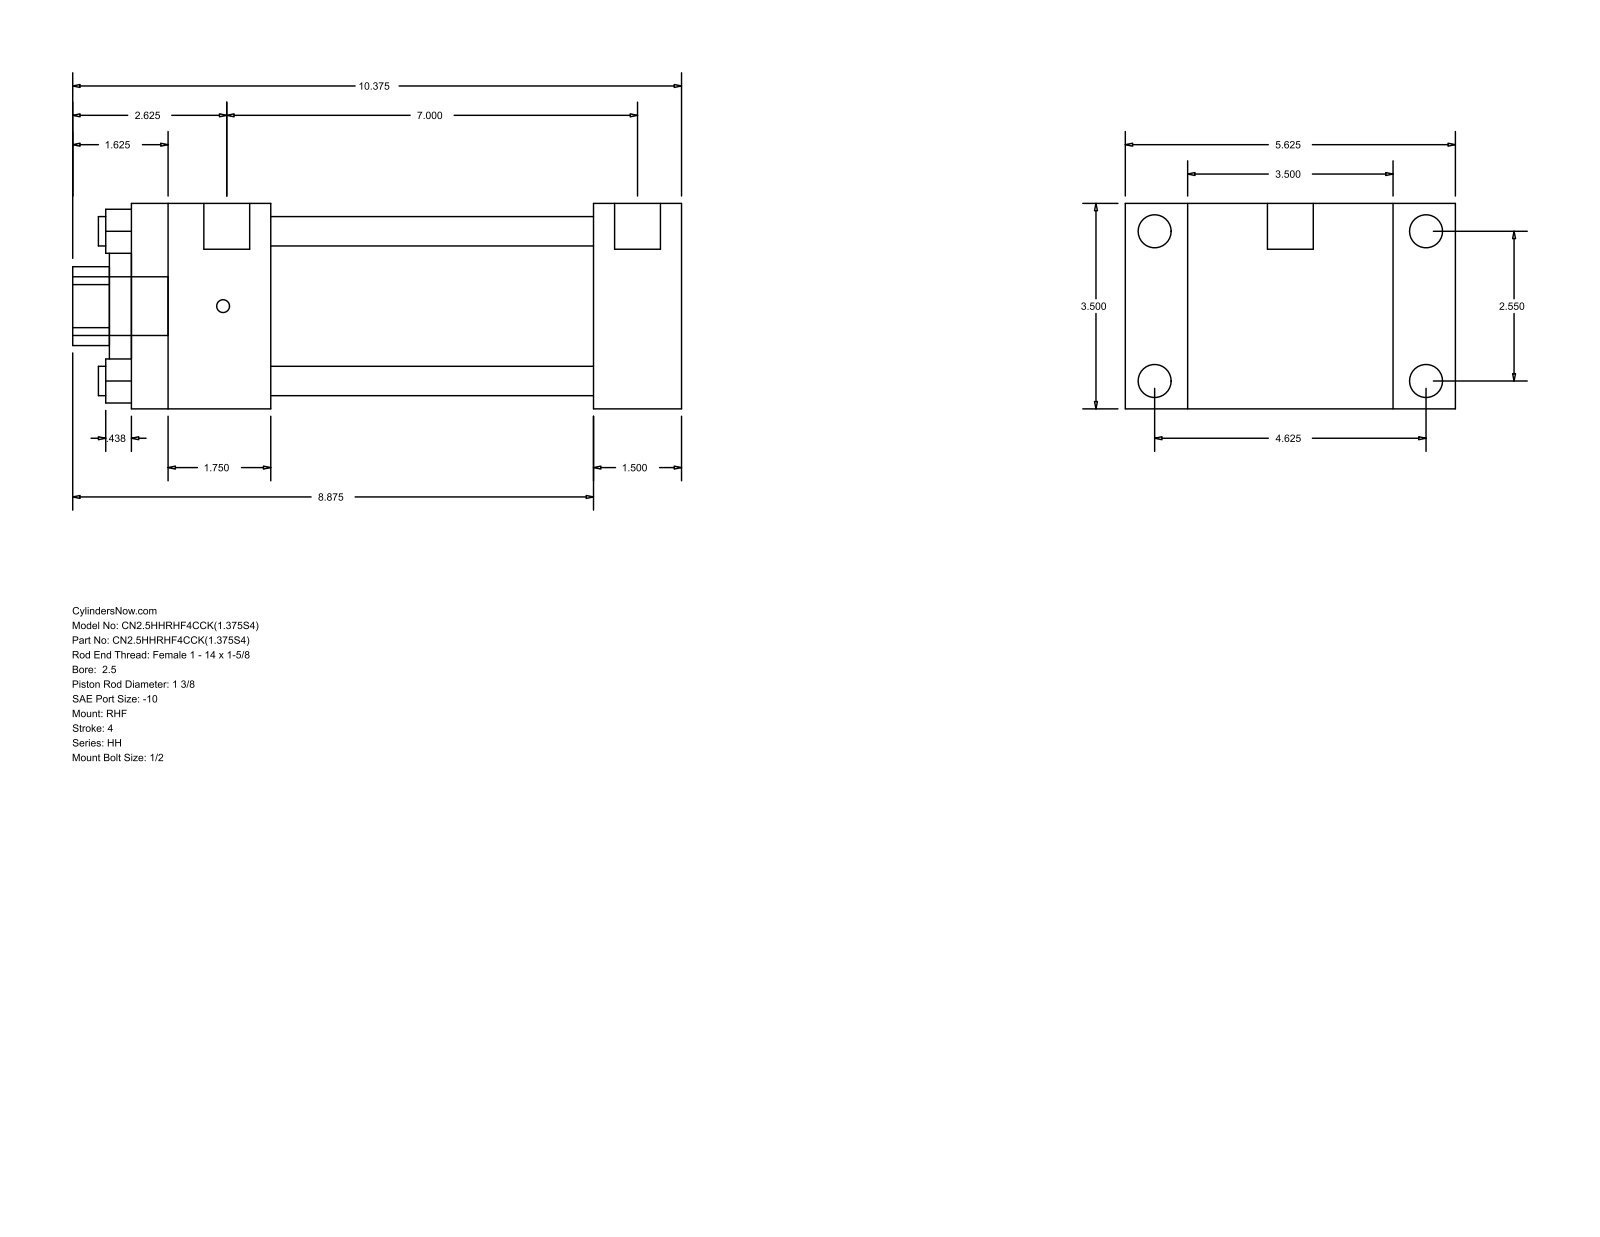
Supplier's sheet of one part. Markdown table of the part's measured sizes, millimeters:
| quantity | value |
| --- | --- |
| part name | HH_RHF__0250_1.375 |
| STEP written by | GSSL Pune (CONFIG_CONTROL_DESIGN) |
| units | millimeters |
| bodies | 0 solids, 88 faces (60 planar, 28 cylindrical, 0 other) |
| overall size | 263.52 × 142.88 × 88.9 |
| round holes (diameter × count) | 12.7 × 4, 34.92 × 1, 50.8 × 1, 73.03 × 1 |
| round bosses / shafts (diameter × count) | 14.3 × 4, 5.56 × 4, 19.84 × 2, 25.4 × 1 |
| partial cylindrical surfaces (radius × count) | 17.06 × 1 |
| main face-to-face distances | 88.9, 38.09, 26.99, 115.89, 200.03, 238.12, 142.88, 60.32, 139.71, 177.8 |
| hole center spacings | 45.79, 64.76, 91.58 |
